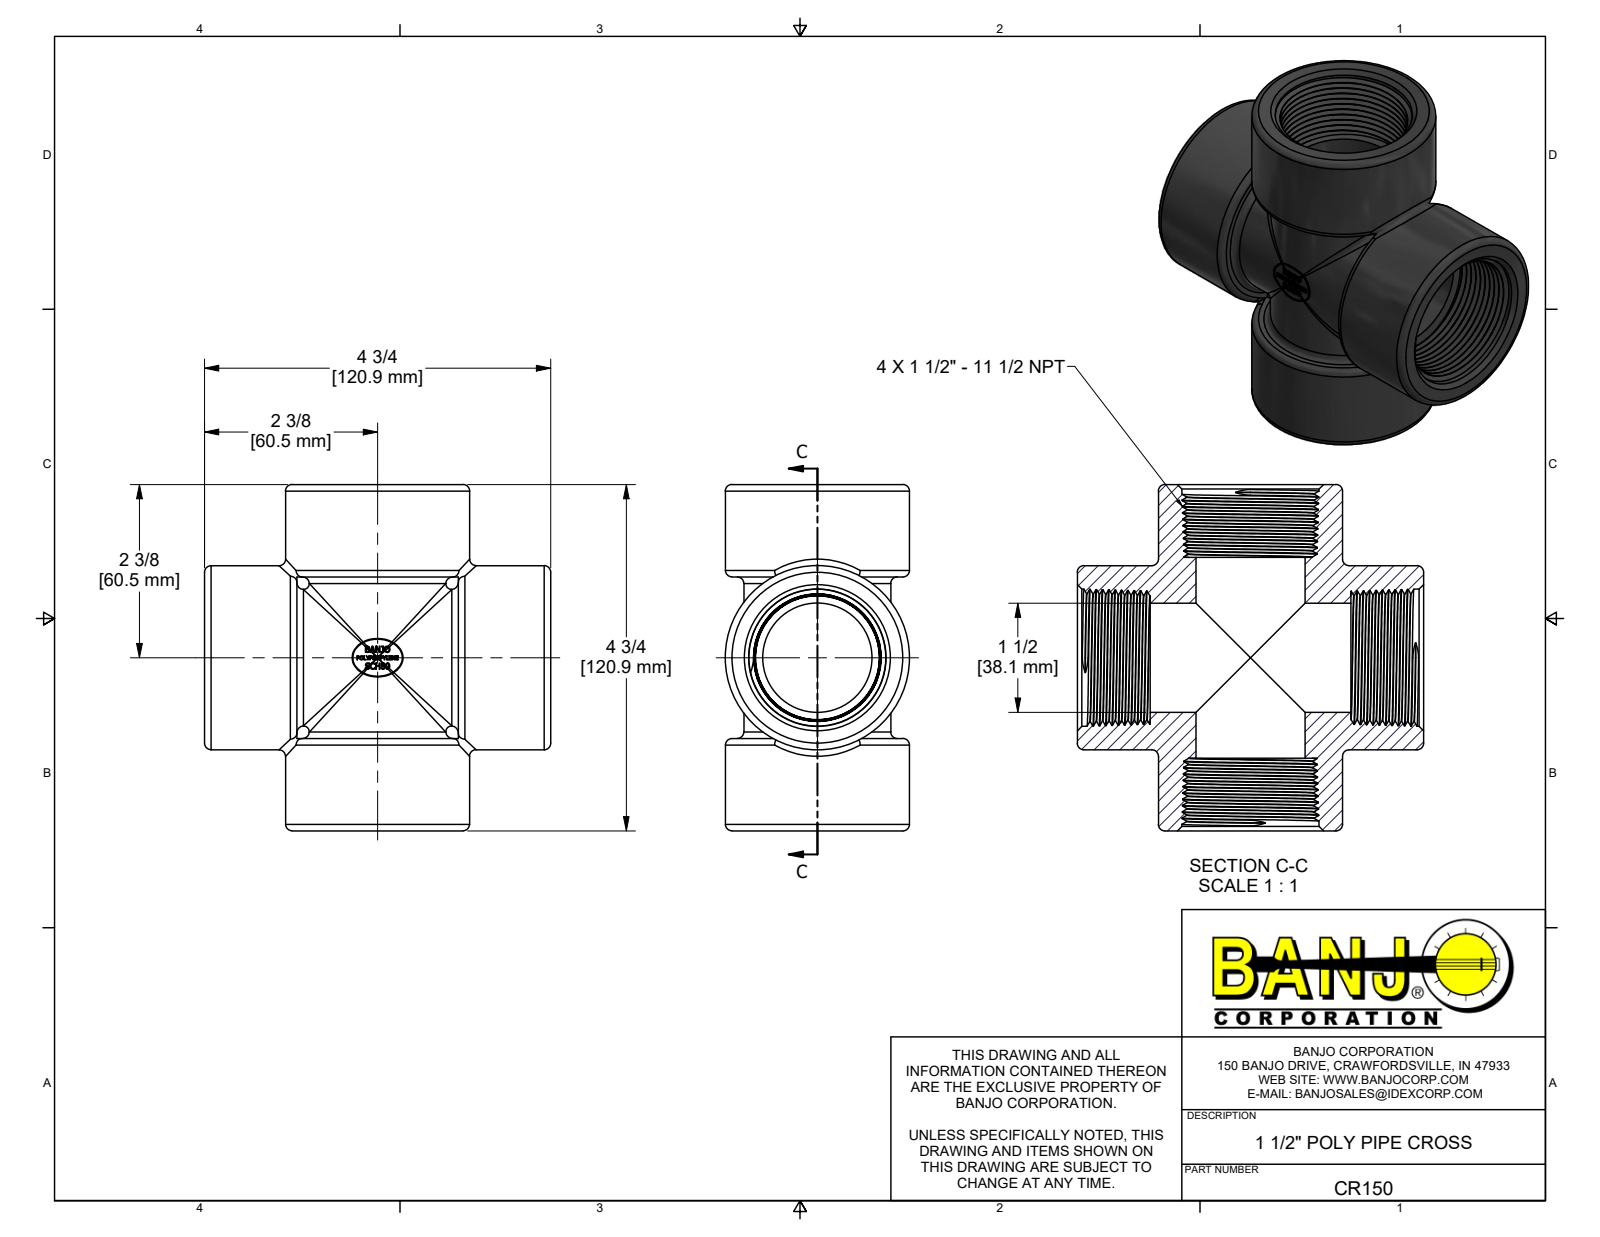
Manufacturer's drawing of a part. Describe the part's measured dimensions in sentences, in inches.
The part is named "CR150". Its 3-D file was written by "Autodesk Inventor 2014 (AUTOMOTIVE_DESIGN)". It is 1 solid with 582 faces: 183 planar, 83 cylindrical and 316 other. Overall it measures 4.76 by 4.76 by 2.53 inches. Its volume is 16.42 cubic inches and its surface area 120.6 square inches. Round holes: 2 of diameter 1.5. Round bosses or shafts: 2 of diameter 2.53. Partial cylindrical surfaces (rounded edges, fillets, slot ends): 2 of radius 0.535, 2 of radius 1.01, 2 of radius 1.02. The main face-to-face distances are 3.76, 1, 4.76, 1.27, 0.27, 3.49, 2.49, 2.76, 2.22, 0.75.
